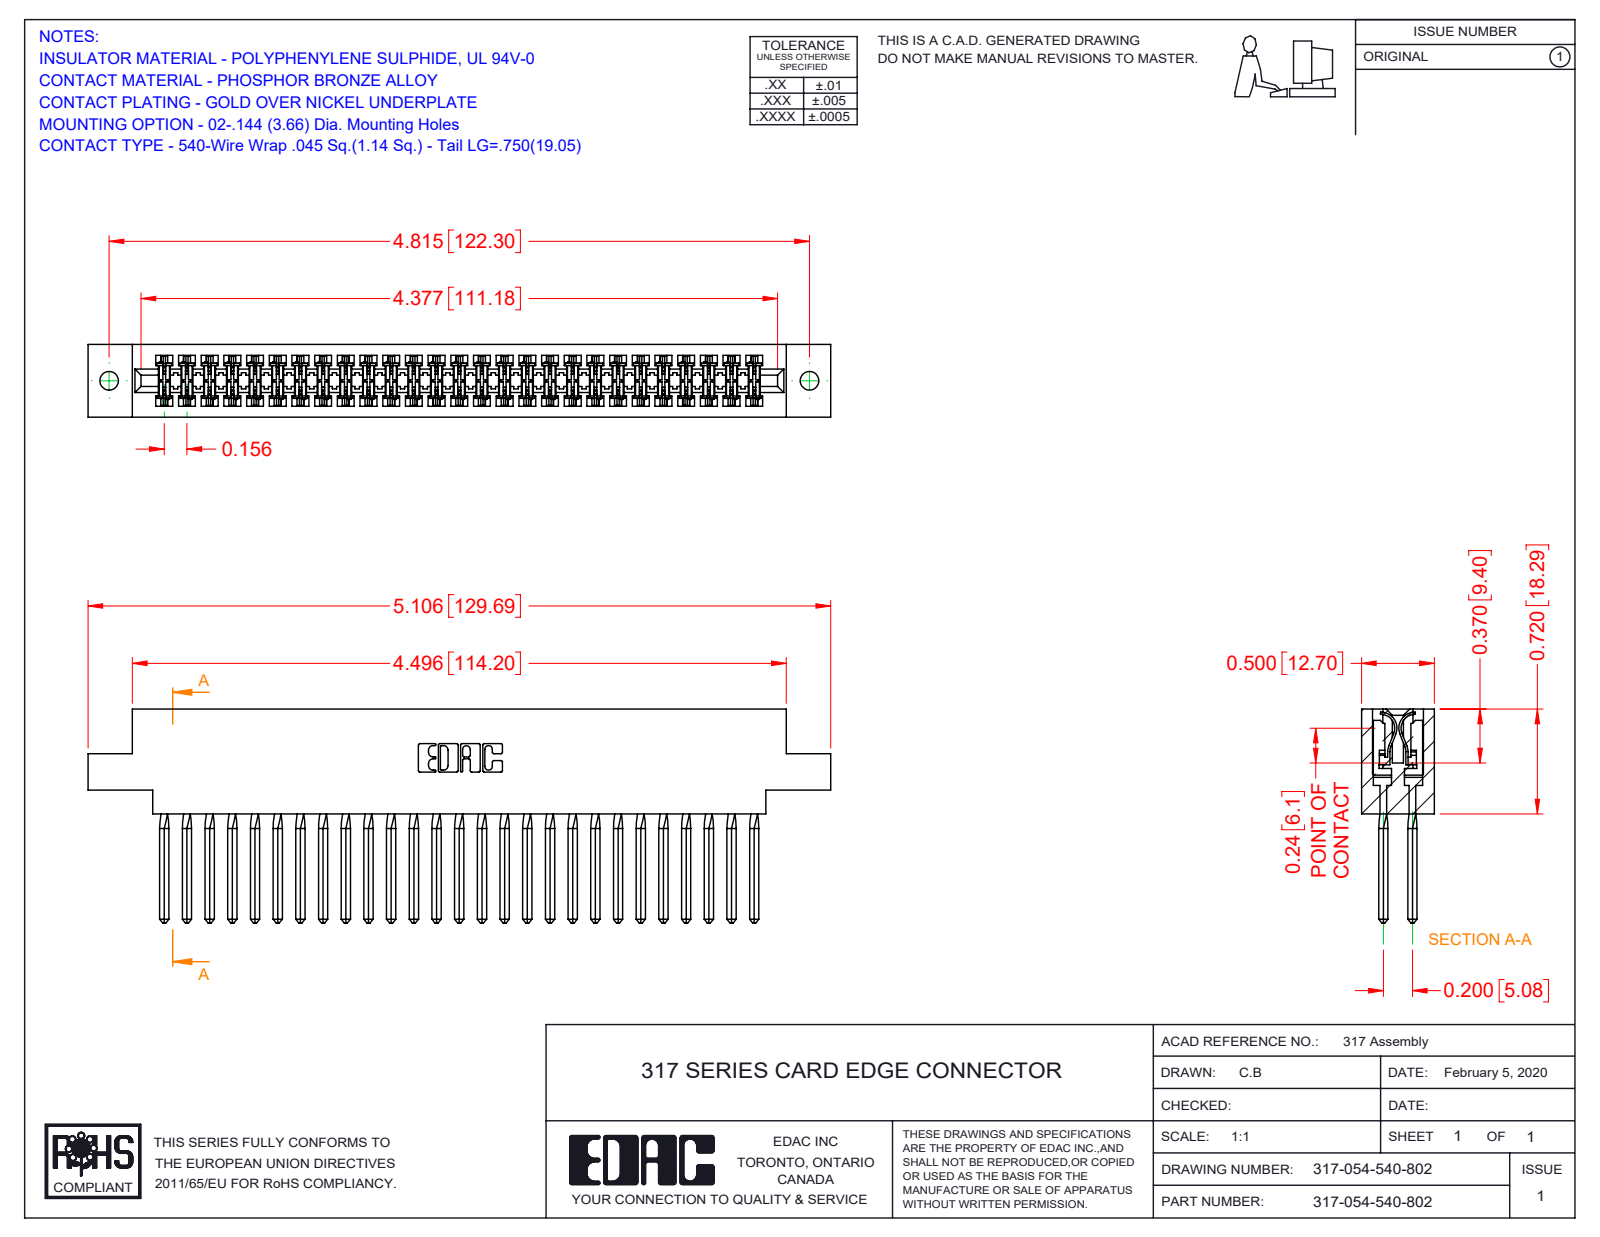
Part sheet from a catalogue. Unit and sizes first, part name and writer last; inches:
Units: inches
Overall size (bounding box): 5.106 × 1.47 × 0.5
Round holes (diameter × count): ⌀0.128 ×2
Partial cylindrical surfaces — rounded edges, fillets, slot ends (radius × count): R0.015 ×108, R0.01 ×22, R0.007 ×6, R0.031 ×6, R0.026 ×3, R0.095 ×2, R0.1 ×2, R0.11 ×2
Main face-to-face distances: 0.5, 0.075, 0.425, 0.35, 0.11, 0.195, 0.094, 0.72, 0.2, 0.115
Hole centre spacings: 4.815
Volume: 1.295 in³ · Surface area: 47.76 in²
Bodies: 55 solids, 4908 faces (4000 planar, 692 cylindrical, 216 other)
Part name (STEP PRODUCT): 317-290-001_540; 317-054-540-802; 317 Part_.144 Dia
STEP written by: SolidWorks 2016 (CONFIG_CONTROL_DESIGN)
